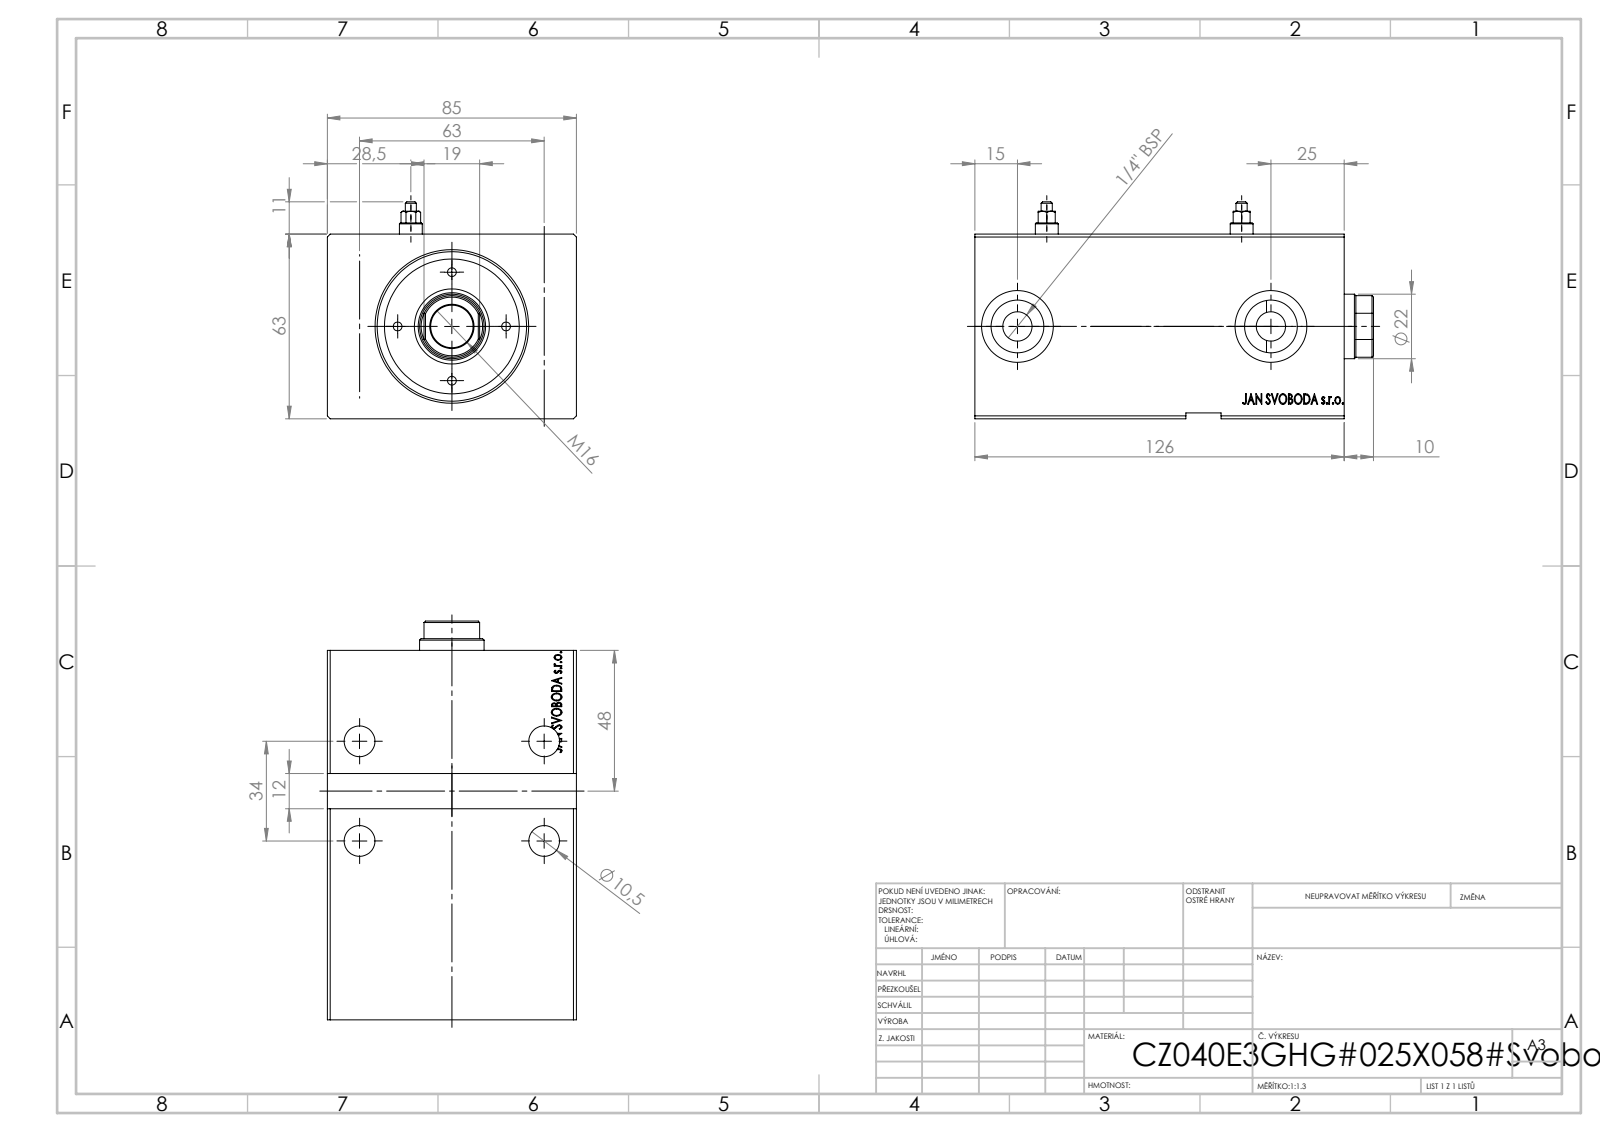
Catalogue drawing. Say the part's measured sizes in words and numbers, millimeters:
Its 3-D file was written by "SolidWorks 2019 (CONFIG_CONTROL_DESIGN)". It is 1 solid with 797 faces: 383 planar, 30 cylindrical and 384 other. Overall it measures 126 by 85 by 63 millimeters. Its volume is 495 935 cubic millimeters and its surface area 71 501 square millimeters. Round holes: 4 of diameter 10.5, 2 of diameter 8, 2 of diameter 10, 2 of diameter 18, 2 of diameter 24.5, 1 of diameter 36, 1 of diameter 40, 1 of diameter 51. The main face-to-face distances are 63, 85, 126, 110.7, 15.3, 2, 61, 125.8, 15.1, 10. The hole center spacings are 34, 63, 71.59, 17.95, 34.73, 40.48, 45.68, 54.5.
